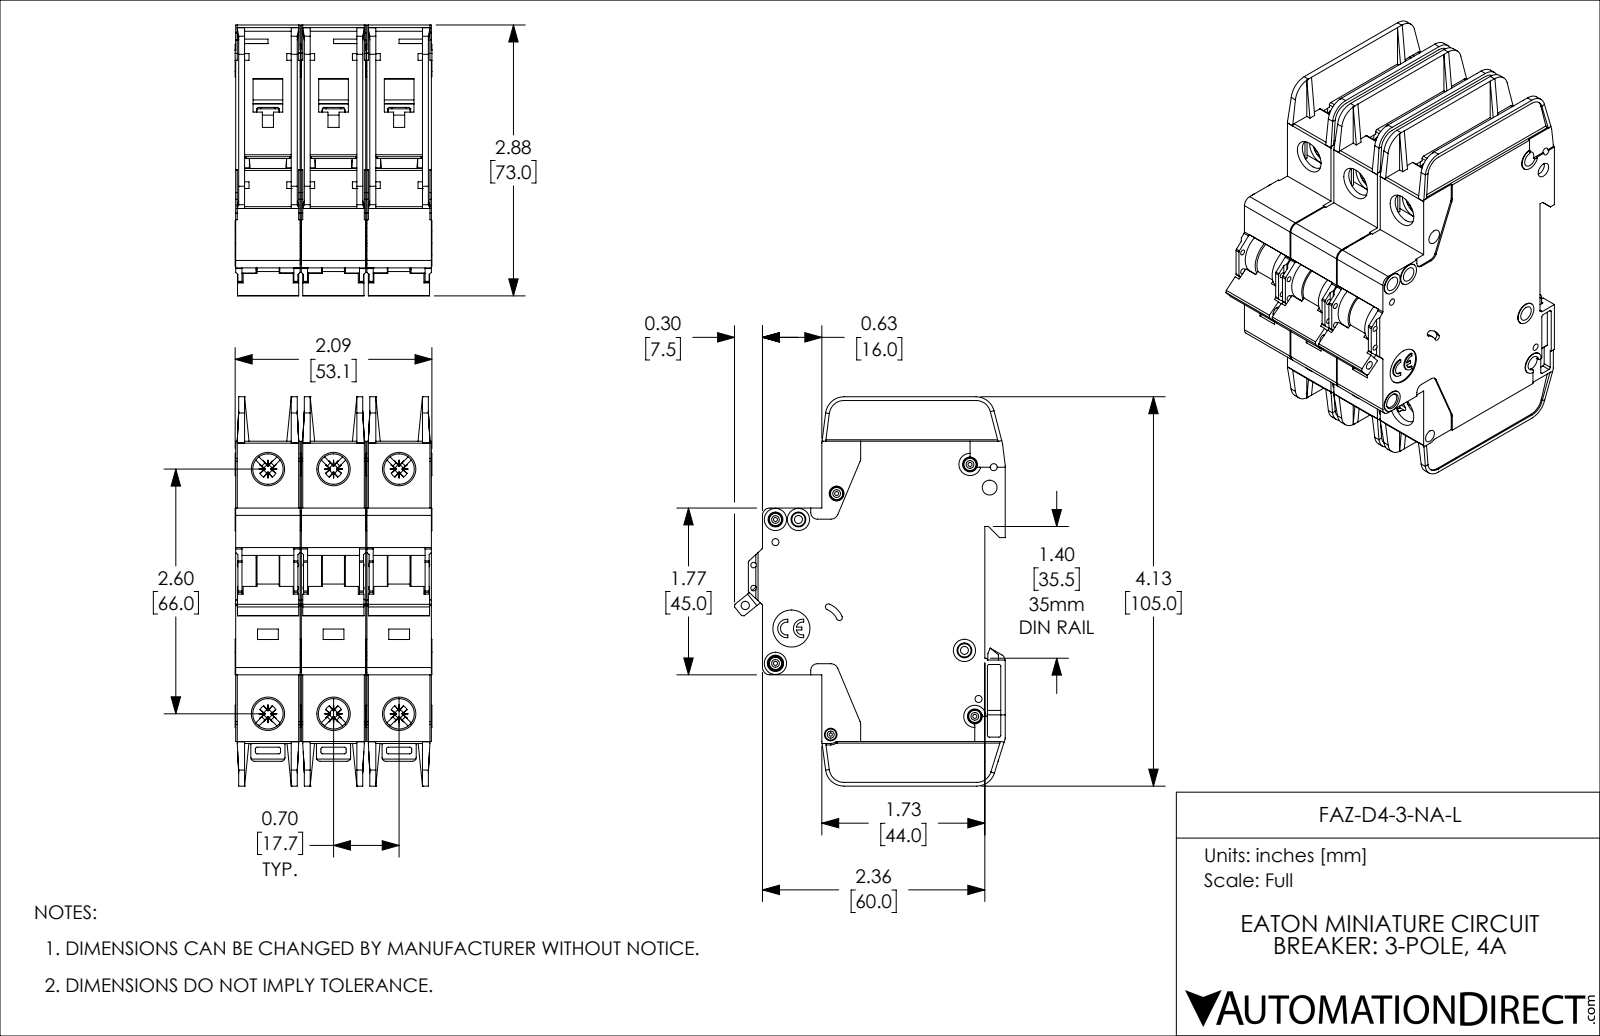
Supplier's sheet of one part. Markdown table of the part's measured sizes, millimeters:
| quantity | value |
| --- | --- |
| part name | FAZ-D4-3-NA-L |
| STEP written by | SolidWorks 2019 (AUTOMOTIVE_DESIGN) |
| units | millimeters |
| bodies | 3 solids, 3381 faces (2013 planar, 1071 cylindrical, 297 other) |
| overall size | 105 × 73.1 × 53.1 |
| volume | 230 200 mm³ |
| surface area | 79 350 mm² |
| round holes (diameter × count) | 4 × 8, 8.2 × 6, 1.1 × 5, 1.9 × 4, 1.5 × 2, 2.2 × 2, 0.9 × 1, 2.3 × 1, 2.5 × 1, 3.4 × 1, 10 × 1 |
| round bosses / shafts (diameter × count) | 3.3 × 5, 6 × 4, 3 × 4, 2.5 × 3 |
| partial cylindrical surfaces (radius × count) | 0.5 × 72, 0.4 × 30, 1 × 18, 1.1 × 12, 2 × 12, 0.2 × 6, 0.3 × 6, 0.7 × 6 |
| main face-to-face distances | 17.7, 1.2, 35.4, 17.4, 15, 35.1, 18.9, 16.5, 2.7, 2.4 |
| hole center spacings | 17.7, 68.3, 66, 6.2, 13.6, 22.1, 35.4, 74.9 |
